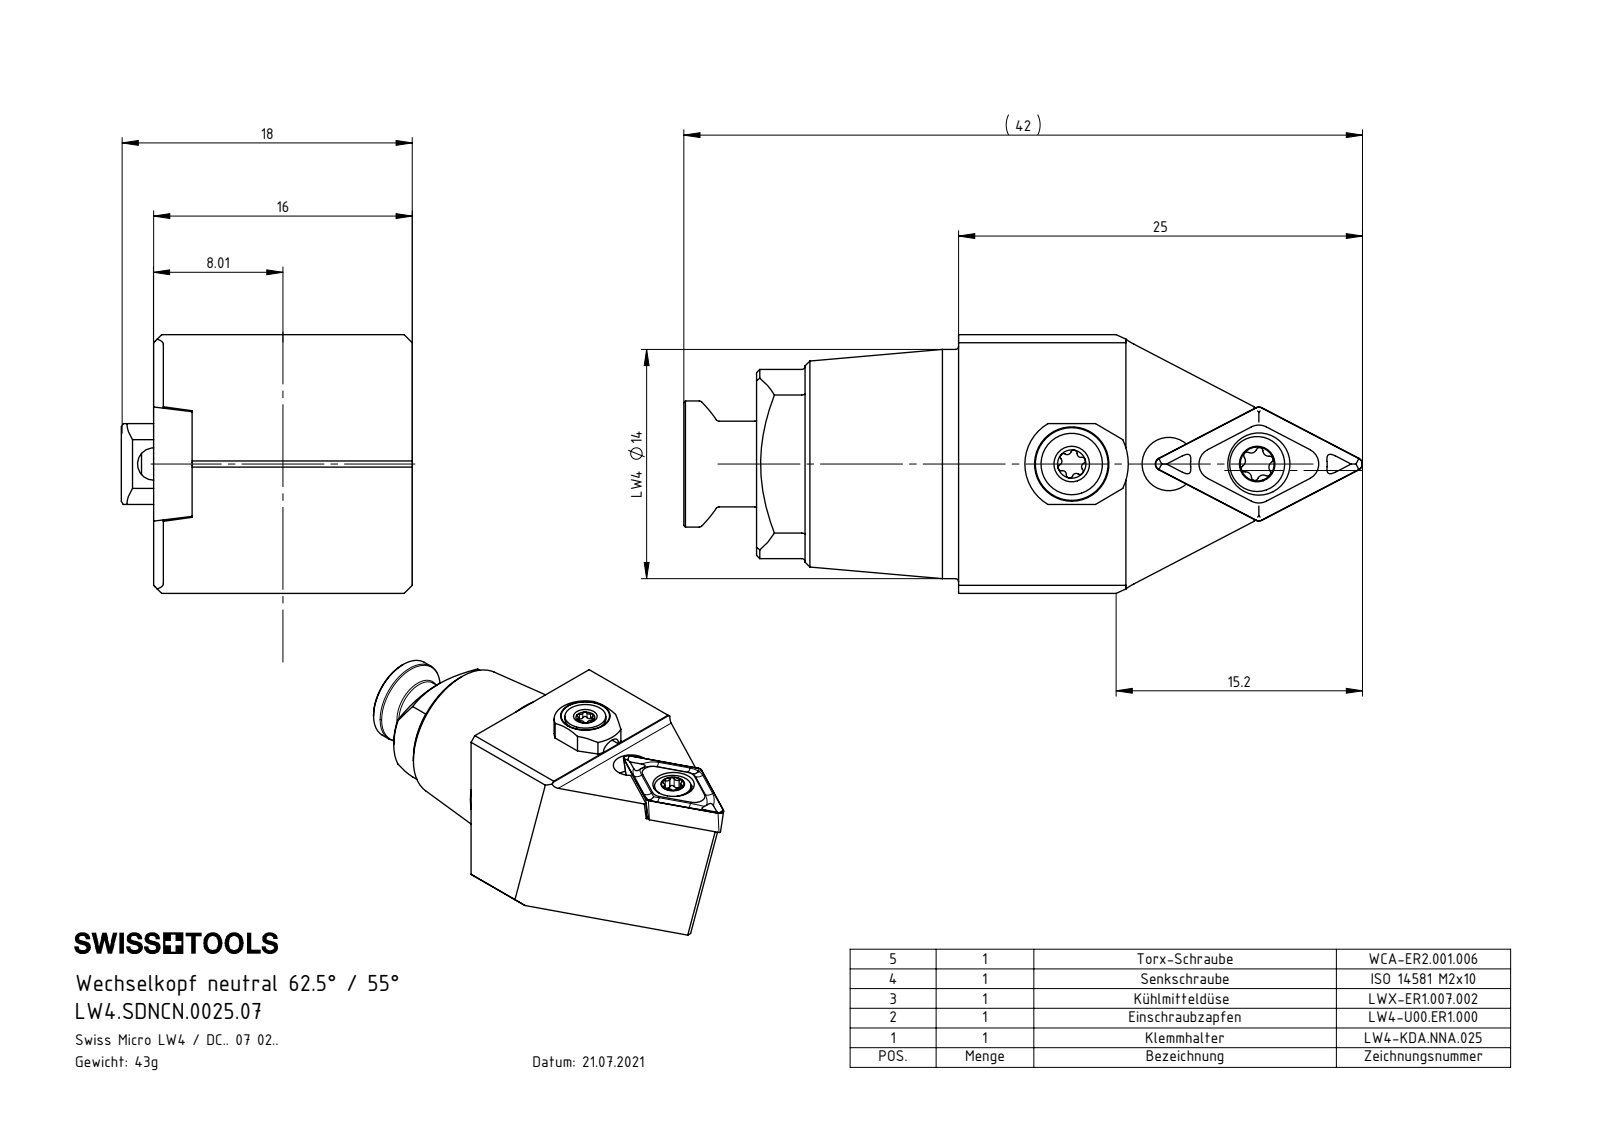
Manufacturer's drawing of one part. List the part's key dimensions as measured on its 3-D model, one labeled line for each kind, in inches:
Part name (STEP PRODUCT): LWX-ER1.007.002; LW4.SDNCN.0025.07; LW4-KDA.NNA.025_A; ISO 14581 - M2x10 (+3 more)
STEP written by: SolidWorks 2022 (CONFIG_CONTROL_DESIGN)
Units: inches
Bodies: 6 solids, 260 faces (69 planar, 81 cylindrical, 110 other)
Overall size (bounding box): 1.653 × 0.709 × 0.63
Volume: 0.338 in³ · Surface area: 5.008 in²
Round holes (diameter × count): ⌀0.118 ×2, ⌀0.063 ×1, ⌀0.079 ×1, ⌀0.081 ×1, ⌀0.098 ×1, ⌀0.11 ×1, ⌀0.13 ×1, ⌀0.152 ×1, ⌀0.217 ×1
Round bosses / shafts (diameter × count): ⌀0.558 ×1, ⌀0.303 ×1, ⌀0.236 ×1, ⌀0.209 ×1, ⌀0.197 ×1, ⌀0.15 ×1, ⌀0.134 ×1, ⌀0.098 ×1
Partial cylindrical surfaces — rounded edges, fillets, slot ends (radius × count): R0.008 ×8, R0.008 ×6, R0.009 ×6, R0.014 ×4, R0.014 ×2, R0.02 ×1, R0.039 ×1, R0.114 ×1
Main face-to-face distances: 0.63, 0.536, 0.094, 0.024, 0.606, 0.07, 0.295, 0.079, 0.492, 0.157
Hole centre spacings: 0.215, 0.22, 0.236, 0.452, 0.456
